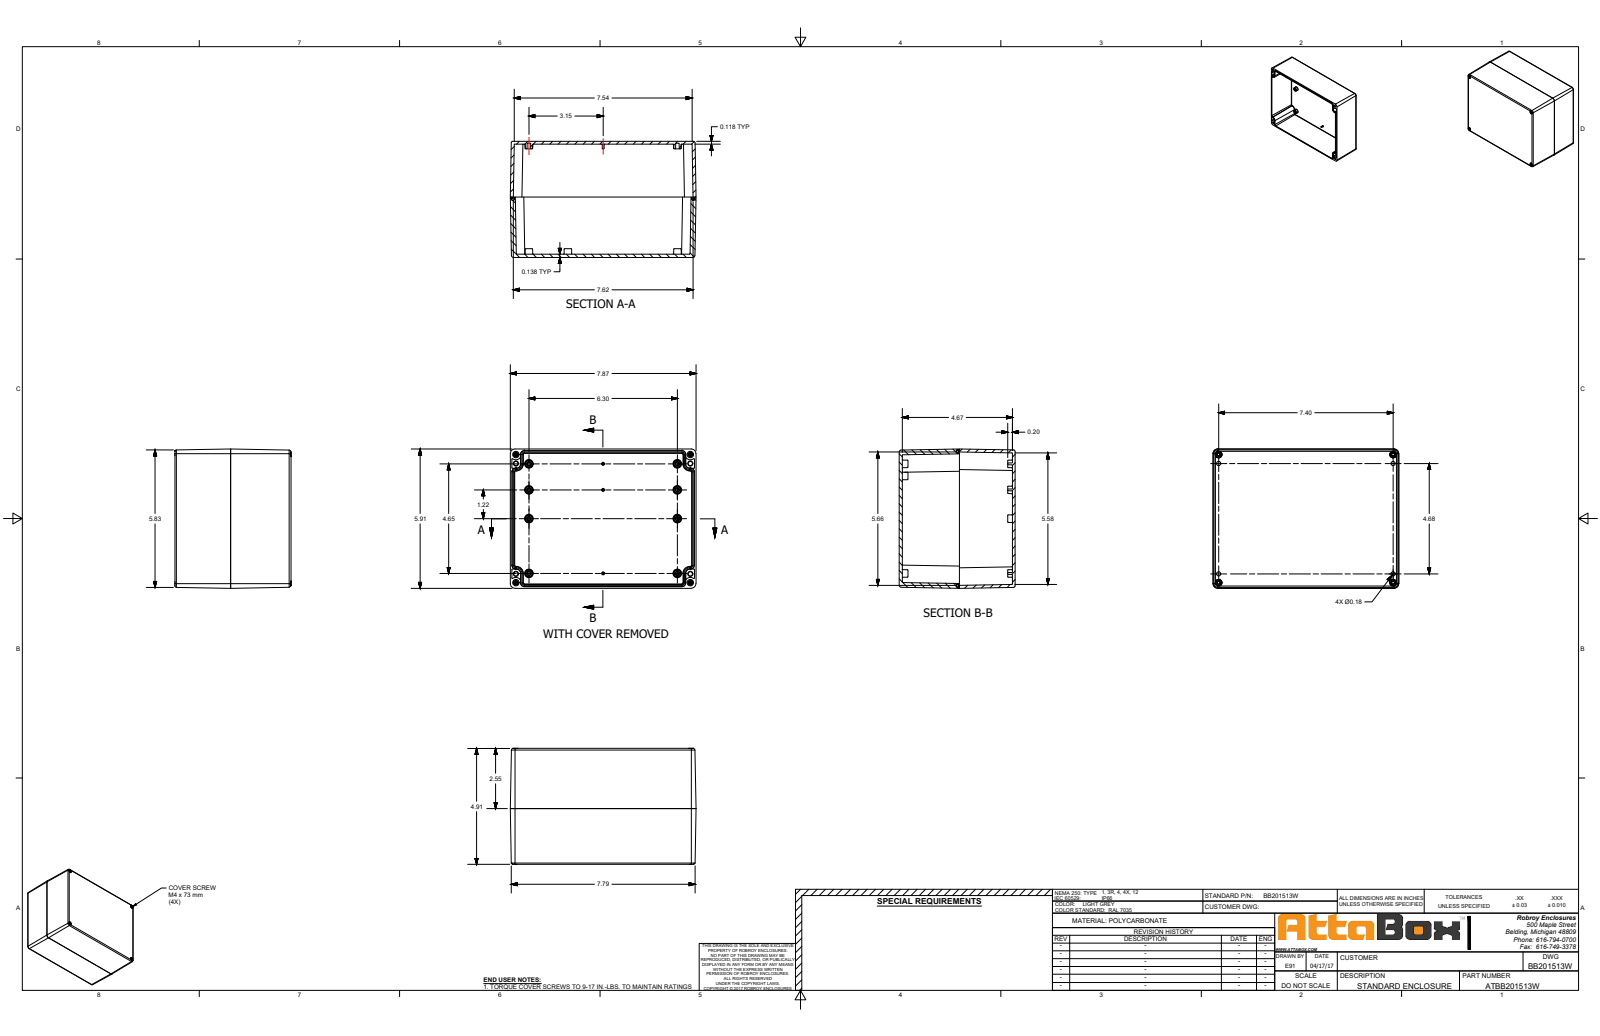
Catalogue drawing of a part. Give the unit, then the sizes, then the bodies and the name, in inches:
Units: inches
Overall size (bounding box): 7.874 × 5.906 × 4.921
Round holes (diameter × count): ⌀0.128 ×4, ⌀0.177 ×4, ⌀0.189 ×4, ⌀0.197 ×4, ⌀0.201 ×4, ⌀0.276 ×4, ⌀0.291 ×4
Round bosses / shafts (diameter × count): ⌀0.268 ×4, ⌀0.173 ×4, ⌀0.157 ×4, ⌀0.13 ×4
Partial cylindrical surfaces — rounded edges, fillets, slot ends (radius × count): R0.055 ×32, R0.02 ×28, R0.039 ×24, R0.079 ×12, R0.201 ×8, R0.059 ×4, R0.094 ×4, R0.102 ×4
Main face-to-face distances: 0.126, 4.921, 0.118, 4.803, 0.138, 4.783, 4.665, 5.906, 5.701, 0.205
Hole centre spacings: 0.378, 5.055, 7.402, 7.411, 8.963, 4.677, 5.433, 8.756
Volume: 34.17 in³ · Surface area: 502.5 in²
Bodies: 11 solids, 1748 faces (652 planar, 428 cylindrical, 668 other)
Part name (STEP PRODUCT): BB201513W
STEP written by: SolidWorks 2018 (AUTOMOTIVE_DESIGN)
